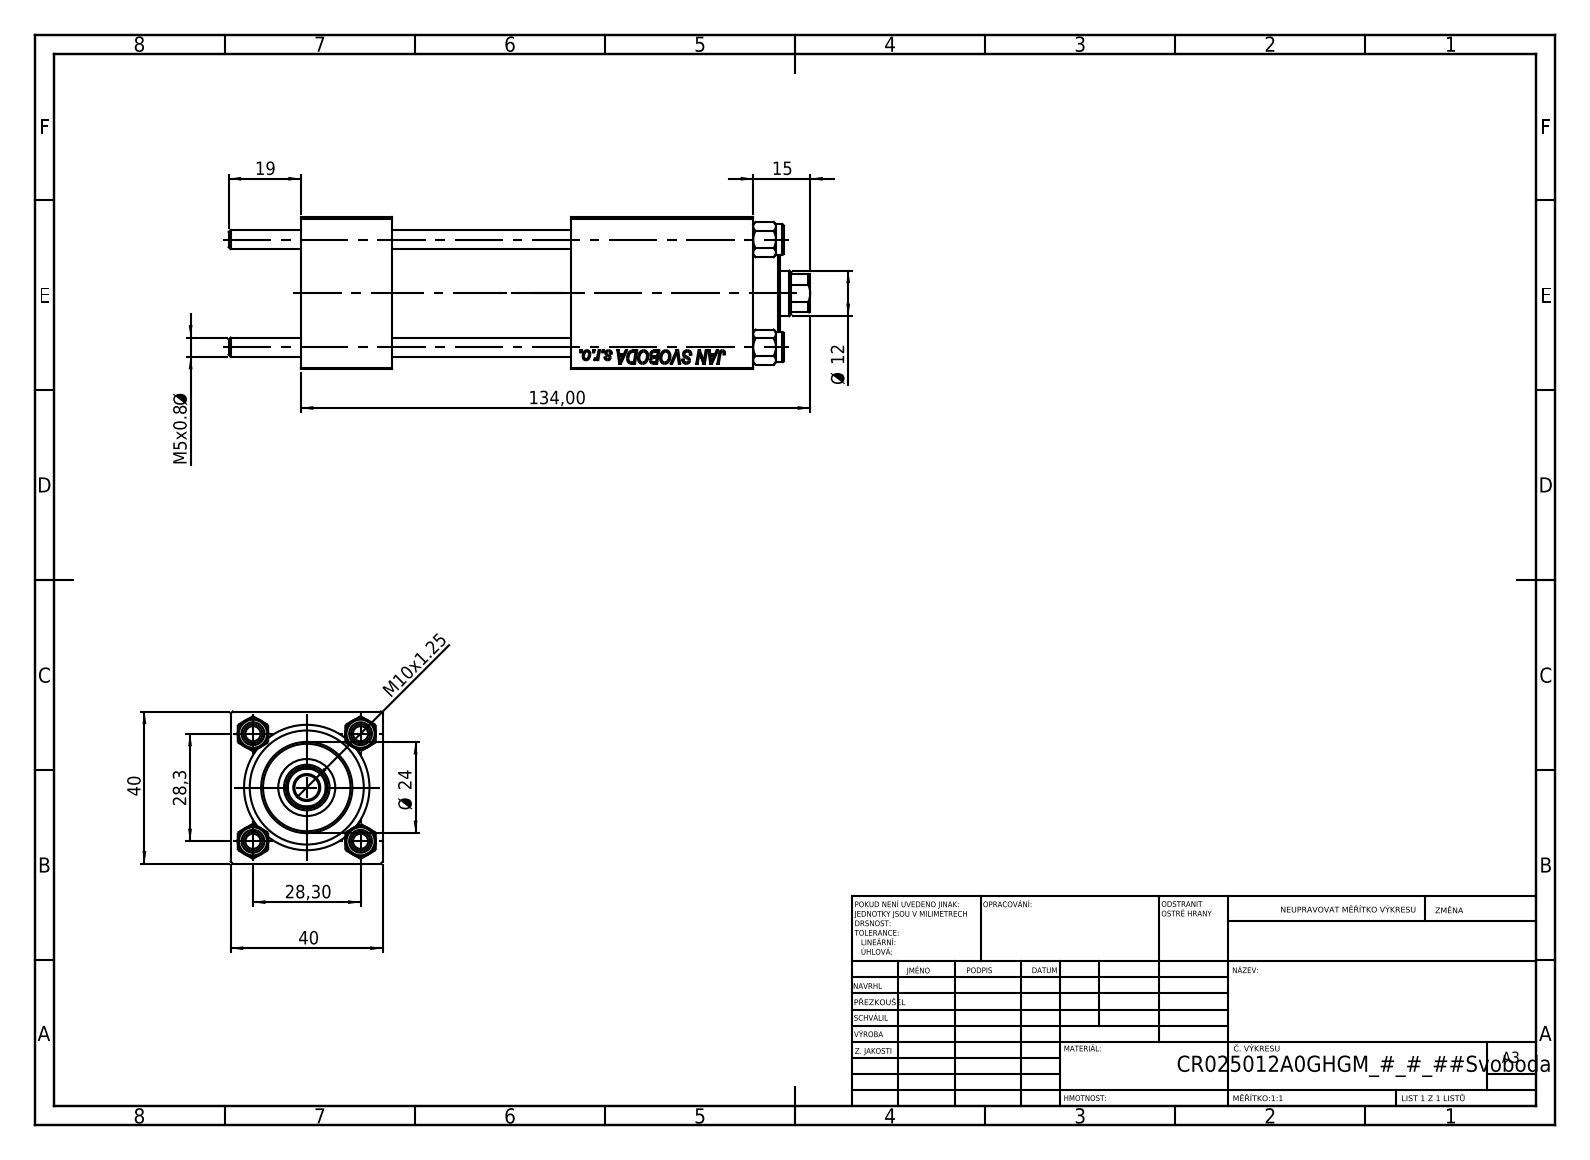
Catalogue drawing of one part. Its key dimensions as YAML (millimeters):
part_name: "V215_VC_A; CR025_012_A_0_G_A_G_M_020_+#_##_TYCINKA; V215CR_BODY_A; V215CR_VCP (+1 more)"
step_written_by: "SolidWorks 2019 (CONFIG_CONTROL_DESIGN)"
units: millimeters
bodies: {solids: 11, faces: 1131, planar: 517, cylindrical: 78, other: 536}
overall_size: [153, 40, 40]
volume: 144824
surface_area: 58872
round_holes:
  - {diameter: 5, count: 4}
  - {diameter: 20, count: 3}
  - {diameter: 7, count: 2}
  - {diameter: 13.16, count: 2}
  - {diameter: 6.5, count: 1}
  - {diameter: 12, count: 1}
  - {diameter: 15, count: 1}
  - {diameter: 25, count: 1}
  - {diameter: 30, count: 1}
round_bosses_or_shafts:
  - {diameter: 8, count: 4}
  - {diameter: 31, count: 1}
  - {diameter: 24, count: 1}
partial_cylinders:
  - {radius: 5.5, count: 1}
face_to_face_distances: [40, 24, 119, 95, 90.3, 66.3, 28.7, 71, 47, 19.3]
hole_center_spacings: [20.01, 28.3, 40.02, 72]
